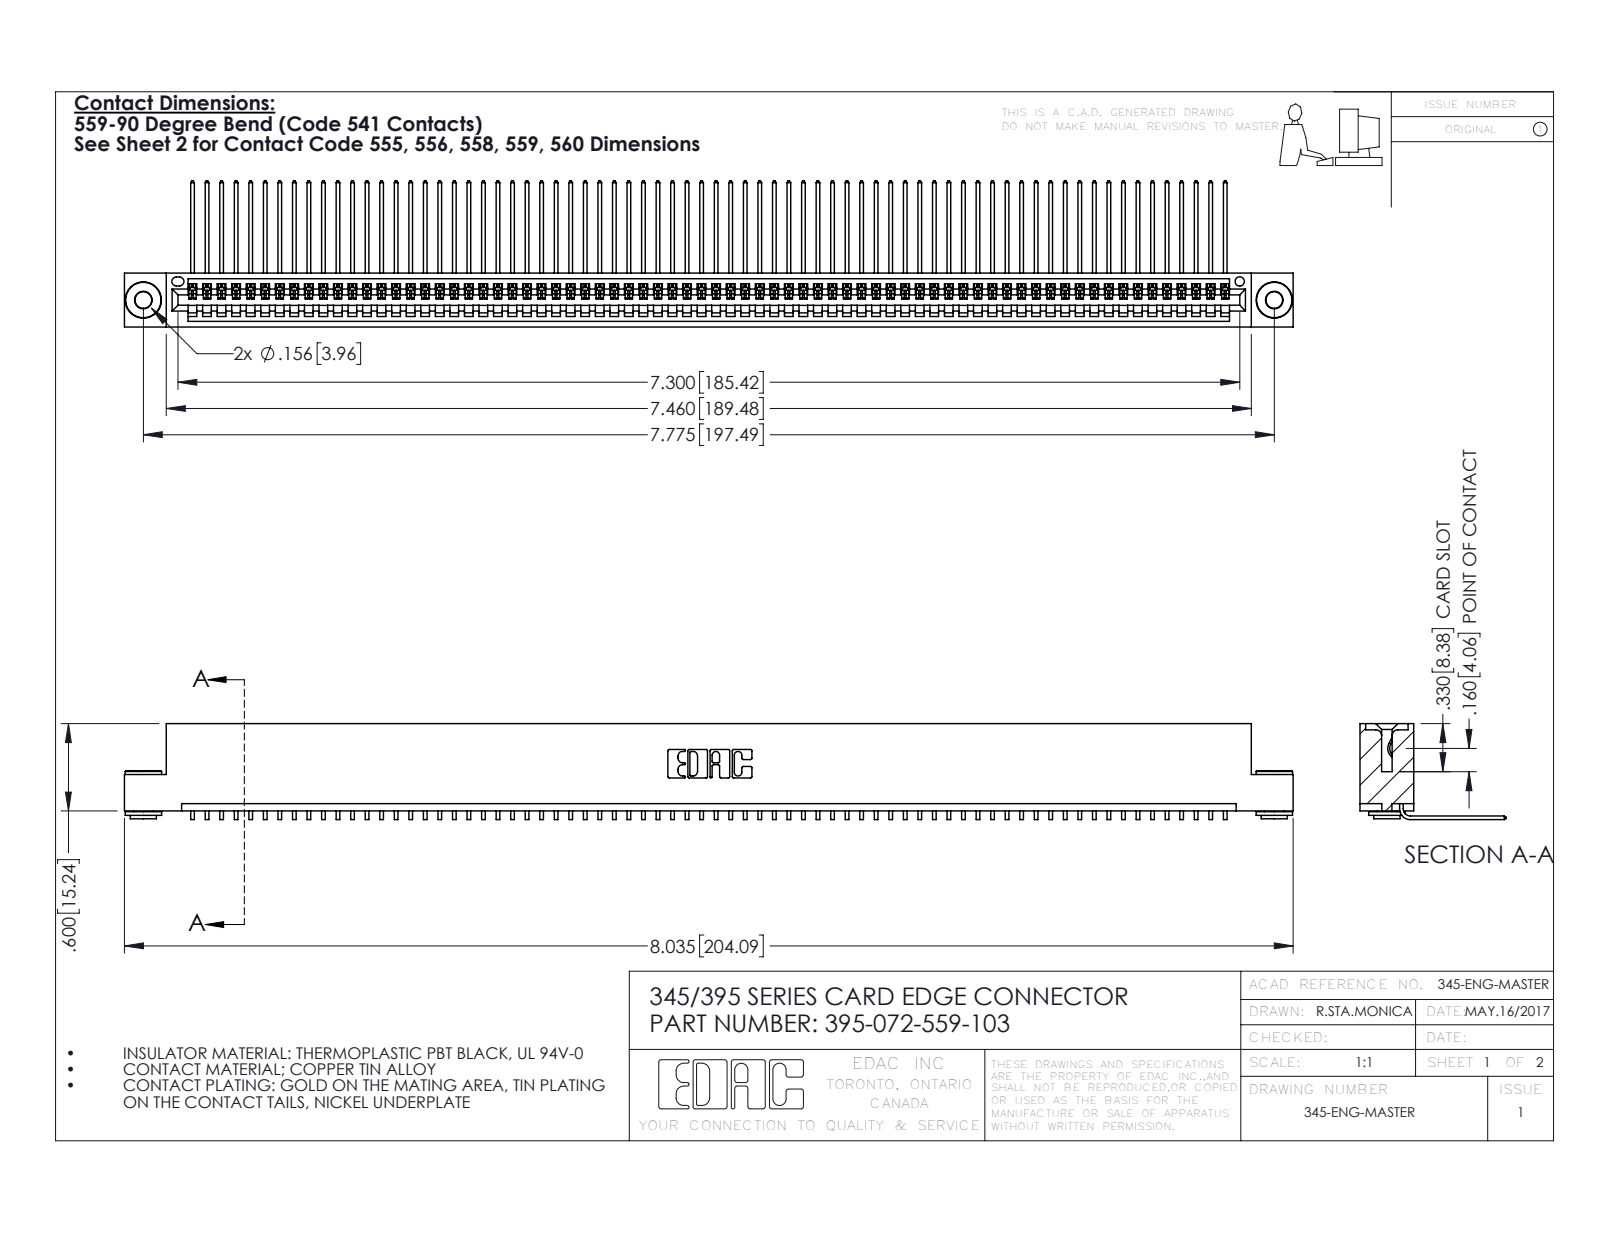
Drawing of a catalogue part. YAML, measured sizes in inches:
part_name: "345 Part_Flush Mounting Lugs - 0.156 Dia-TH; 345-250-002_345-250-002-102; 395-072-559-103; 345-292-001_558 559 Tail - 1"
step_written_by: "SolidWorks 2016 (CONFIG_CONTROL_DESIGN)"
units: inches
bodies: {solids: 75, faces: 4484, planar: 3114, cylindrical: 1362, other: 8}
overall_size: [8.035, 1.005, 0.659]
volume: 1.214
surface_area: 44.12
round_holes:
  - {diameter: 0.116, count: 2}
  - {diameter: 0.156, count: 2}
  - {diameter: 0.064, count: 1}
round_bosses_or_shafts:
  - {diameter: 0.25, count: 2}
  - {diameter: 0.18, count: 2}
  - {diameter: 0.136, count: 2}
partial_cylinders:
  - {radius: 0.006, count: 144}
  - {radius: 0.01, count: 22}
  - {radius: 0.007, count: 6}
  - {radius: 0.031, count: 6}
  - {radius: 0.026, count: 3}
  - {radius: 0.031, count: 2}
  - {radius: 0.04, count: 2}
  - {radius: 0.014, count: 1}
face_to_face_distances: [0.072, 0.298, 0.37, 0.2, 0.025, 0.098, 0.272, 0.225, 0.149, 0.072]
hole_center_spacings: [0.27, 7.539, 7.775]
